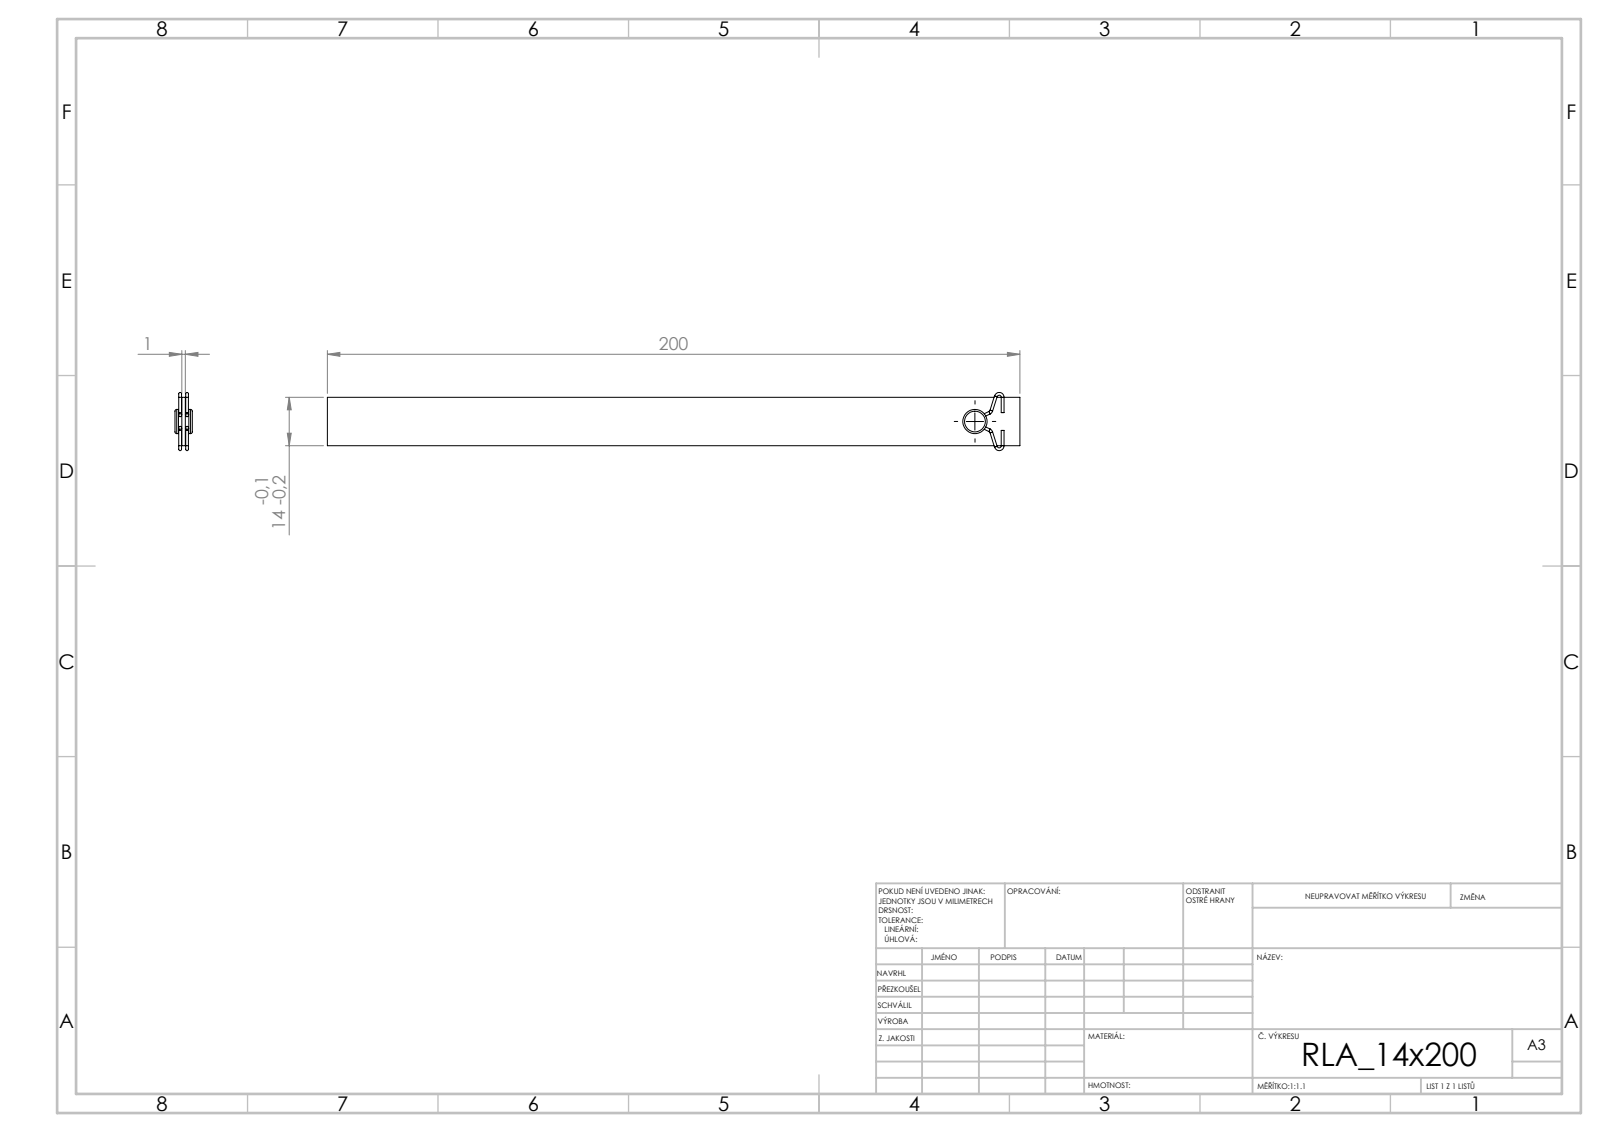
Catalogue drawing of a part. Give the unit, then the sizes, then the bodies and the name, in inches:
Units: inches
Overall size (bounding box): 7.874 × 0.661 × 0.197
Round bosses / shafts (diameter × count): ⌀0.031 ×14, ⌀0.276 ×1, ⌀0.157 ×1
Main face-to-face distances: 0.039, 0.551, 0.079, 0.118, 0.157, 0.197, 7.874, 0.175, 0.376, 0.201
Volume: 0.18 in³ · Surface area: 9.926 in²
Bodies: 3 solids, 82 faces (14 planar, 40 cylindrical, 28 other)
STEP written by: SolidWorks 2019 (CONFIG_CONTROL_DESIGN)
